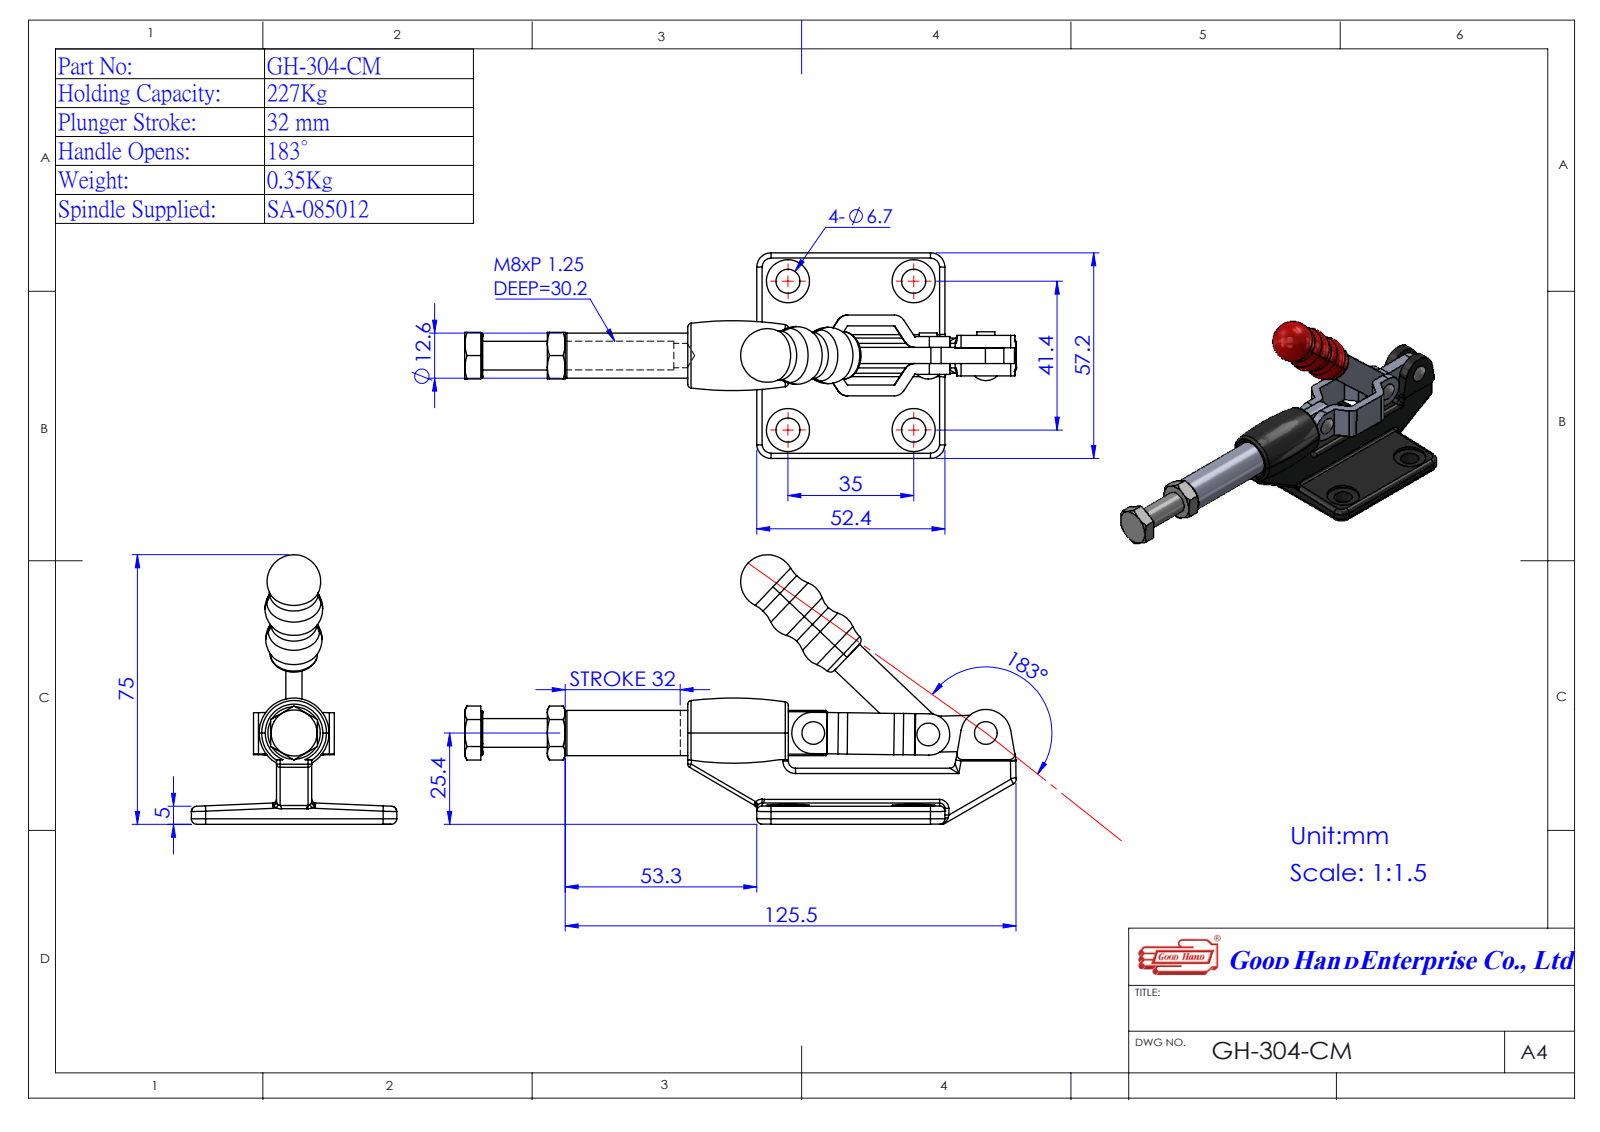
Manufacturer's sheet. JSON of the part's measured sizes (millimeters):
{"part_name": "4304CM33-1^GH-304-CM(簡化)-1; Group1^GH-304-CM(簡化)-1; Group2^GH-304-CM(簡化)-1; GH-304-CM(簡化)-1 (+2 more)", "step_written_by": "SolidWorks 2016 (AUTOMOTIVE_DESIGN)", "units": "millimeters", "bodies": {"solids": 5, "faces": 263, "planar": 89, "cylindrical": 91, "other": 83}, "overall_size": [153.56, 75, 57.2], "volume_mm3": 51545, "surface_area_mm2": 25209, "round_holes": [[6.7, 4], [3.5, 3], [6.8, 1], [12.6, 1]], "round_bosses_or_shafts": [[5, 3], [12.58, 1], [12.5, 1], [8, 1]], "partial_cylinders_radius": [[1.5, 12], [1, 8], [0.1, 6], [4, 5], [0.21, 2], [0.4, 2], [1.1, 2], [5.75, 2]], "face_to_face_distances": [3, 2.7, 7.1, 9.8, 4.5, 2.6, 7.2, 13.5, 6, 16.5], "hole_center_spacings": [35, 41.4, 54.21, 16.06, 31.99, 48.04]}
